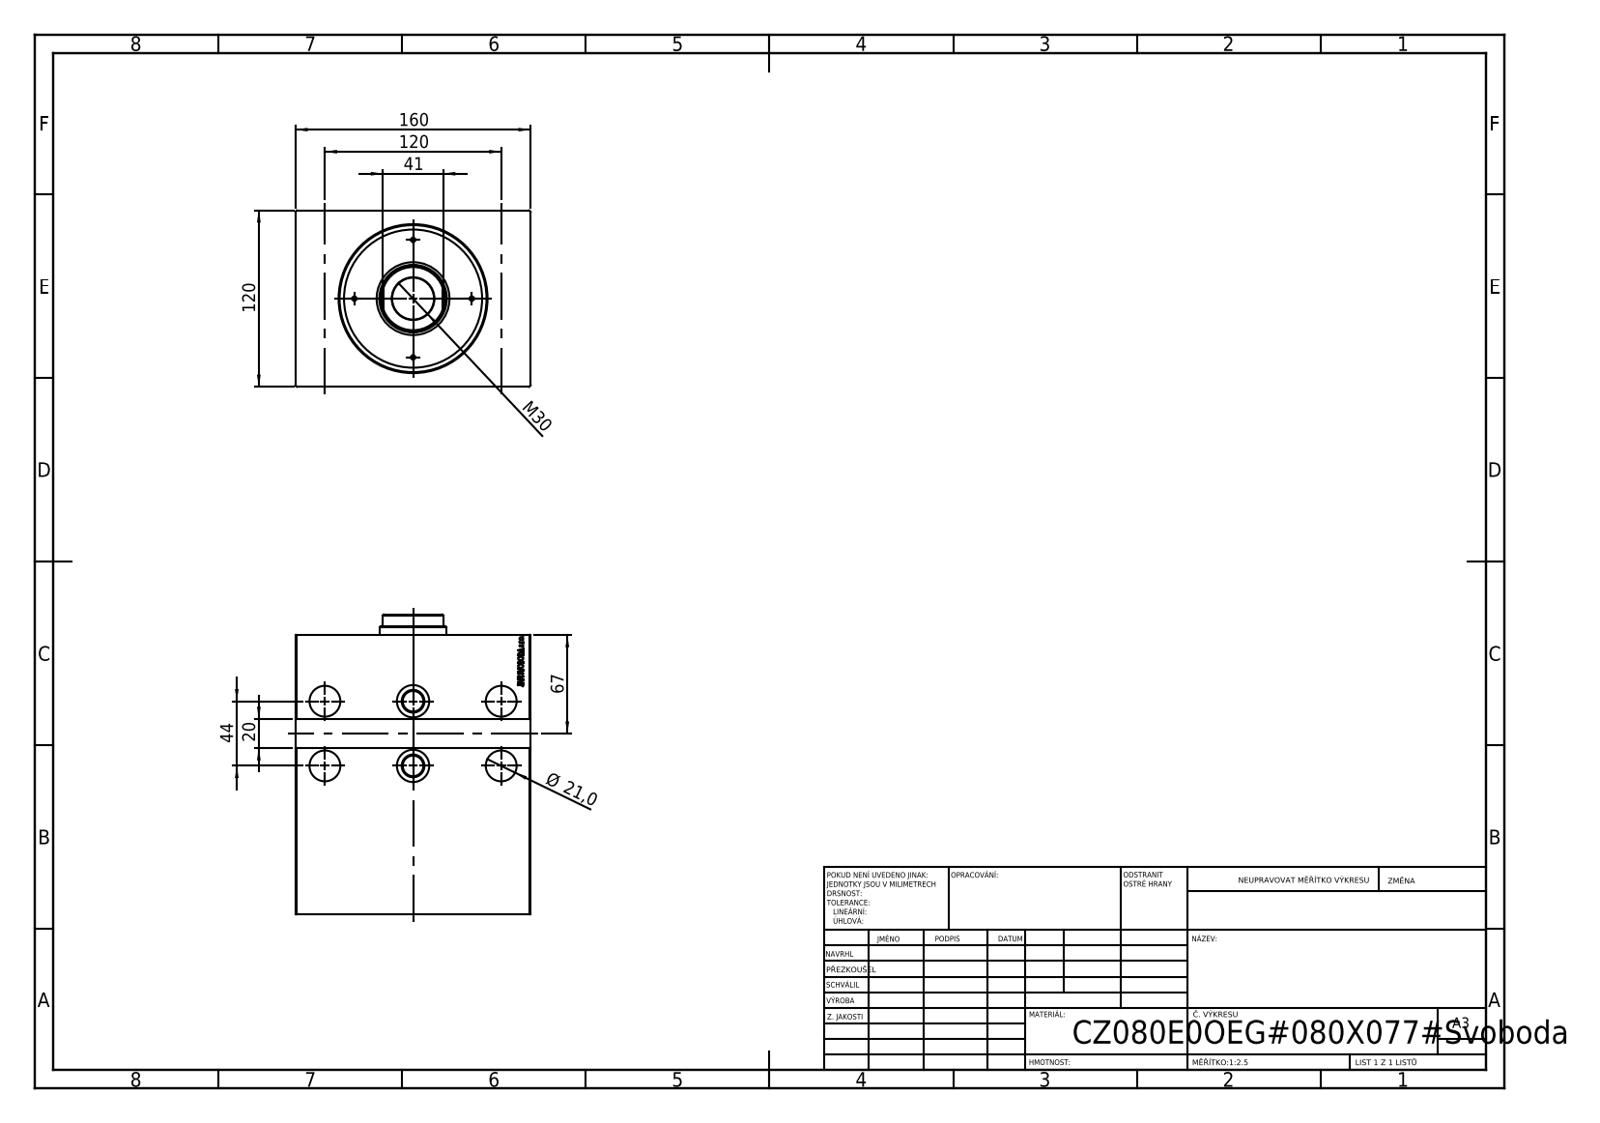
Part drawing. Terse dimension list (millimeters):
written by: SolidWorks 2019 (CONFIG_CONTROL_DESIGN)
unit: mm
bodies: 1 solid, 807 faces (395 planar, 30 cylindrical, 382 other)
size: 190 × 160 × 120
volume: 2 605 000 mm³; area: 216 927 mm²
holes: 4× ⌀21, 2× ⌀8, 2× ⌀14, 2× ⌀22, 1× ⌀36, 1× ⌀80, 1× ⌀100
bosses: 2× ⌀15.5
face distances: 120, 160, 190, 164.7, 25.3, 2, 118, 14, 150.7, 176
hole spacings: 60, 74.4, 44, 120, 127.81, 26.02, 34.01, 50.25
